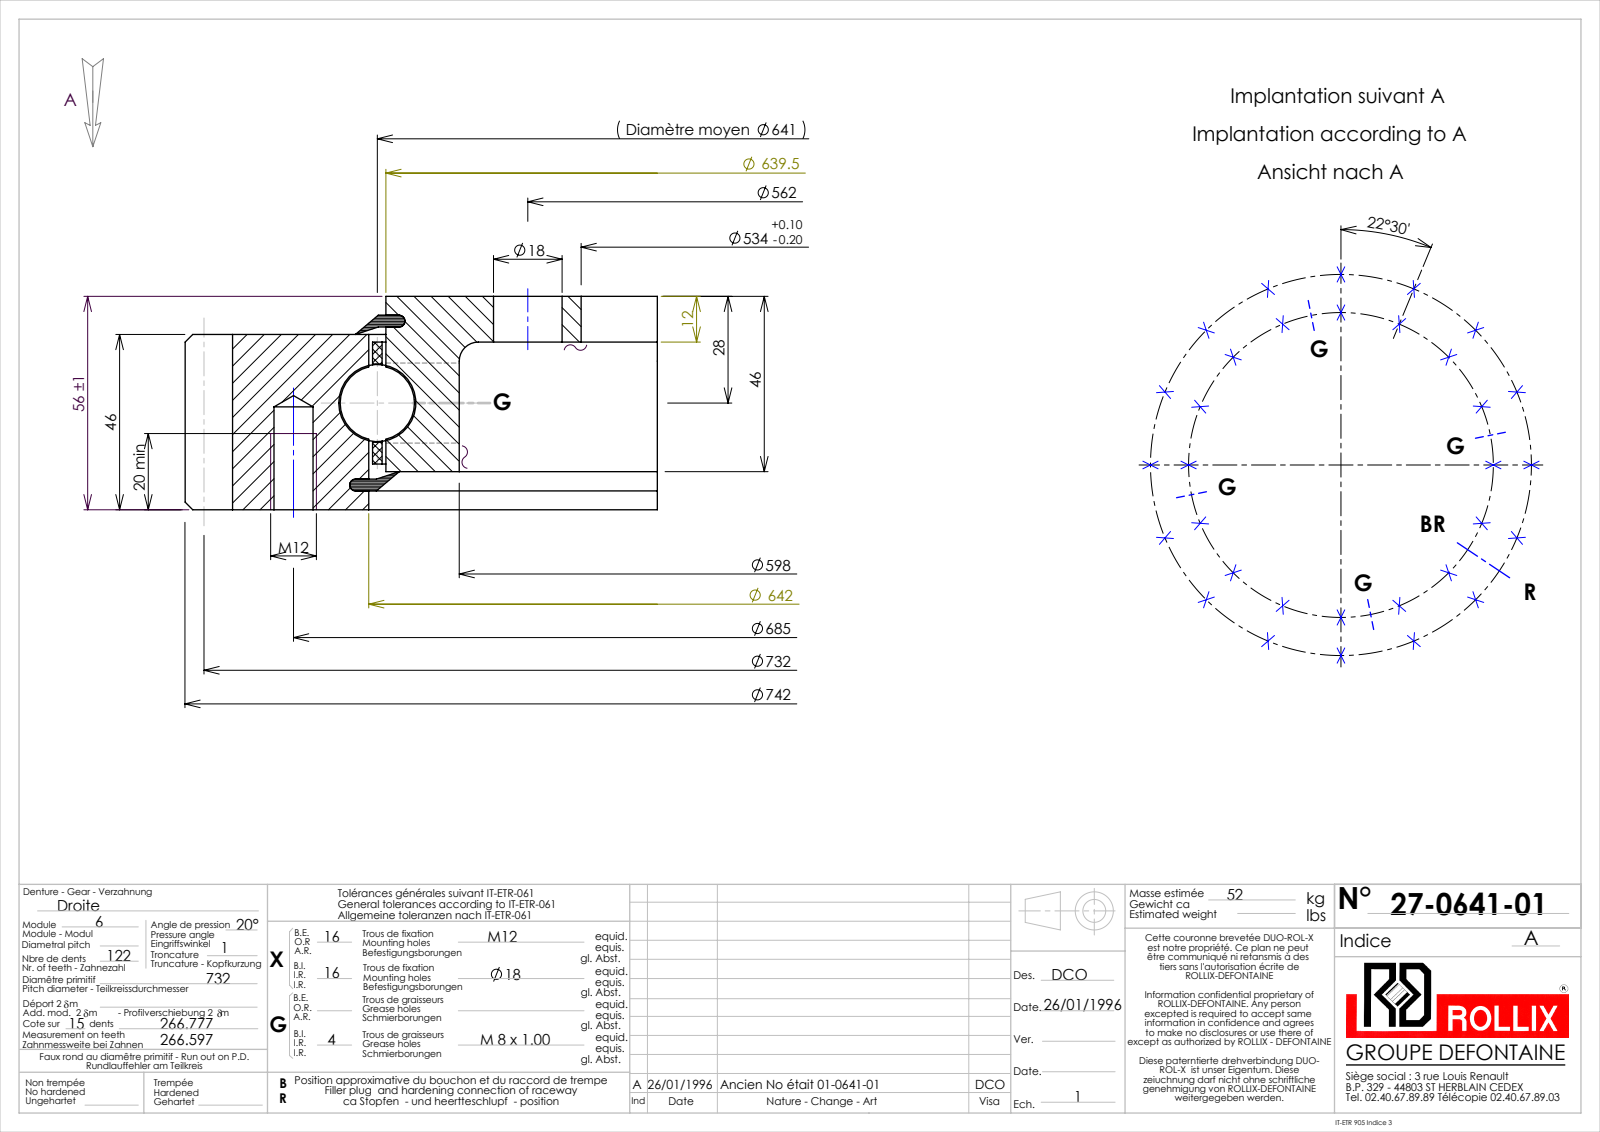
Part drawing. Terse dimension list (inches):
name: 21-0641-01
written by: SolidWorks 2016 (CONFIG_CONTROL_DESIGN)
unit: in
bodies: 9 solids, 984 faces (297 planar, 341 cylindrical, 346 other)
size: 29.213 × 29.208 × 2.205
volume: 378.5 in³; area: 1 620 in²
holes: 16× ⌀0.404, 16× ⌀0.709, 4× ⌀0.276, 1× ⌀21.024, 1× ⌀23.543, 1× ⌀25.413
bosses: 4× ⌀0.315, 1× ⌀25.059
rounds: 1× R14.114, 1× R14.606
face distances: 0.394, 1.811, 2.205, 1.732, 0.079, 0.472, 1.339, 1.417, 0.195, 2.01
hole spacings: 5.345, 17.442, 22.698, 24.08, 5.261, 10.32, 20.454, 9.656
